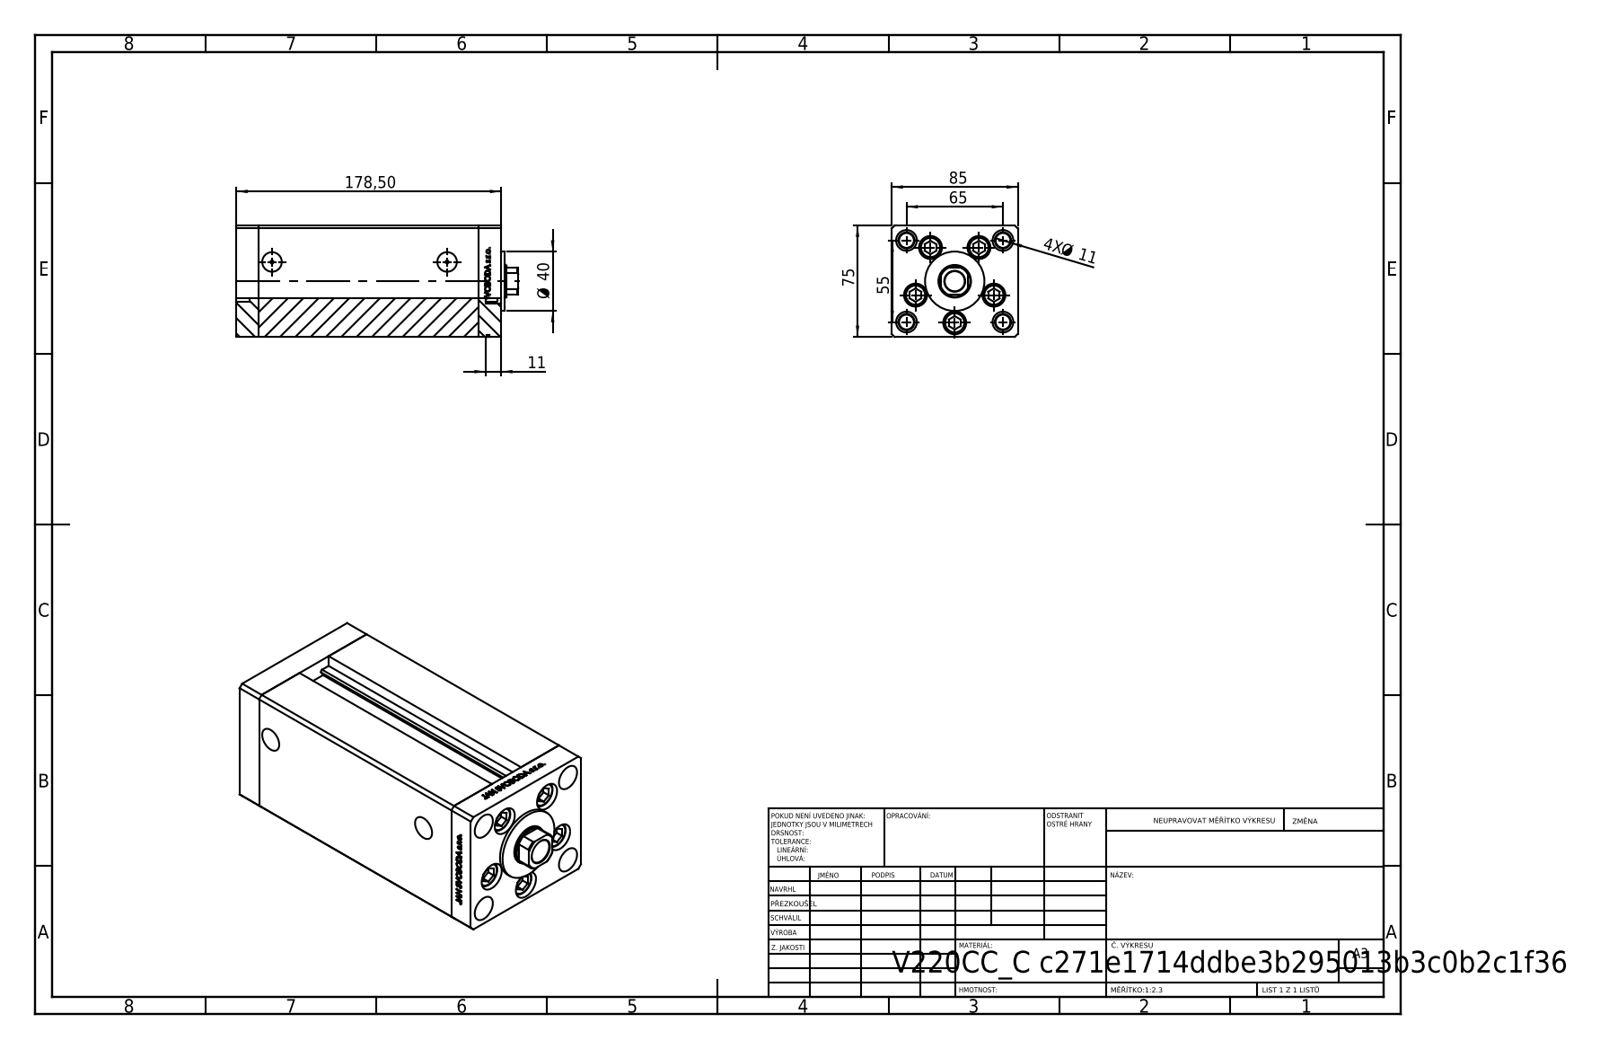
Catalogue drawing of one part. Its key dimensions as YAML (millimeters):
part_name: "V220C_VC_C; V220C_C MIDDLE; V220C FRONT; V220C BACK_C (+1 more)"
step_written_by: "SolidWorks 2019 (CONFIG_CONTROL_DESIGN)"
units: millimeters
bodies: {solids: 13, faces: 1171, planar: 542, cylindrical: 167, other: 462}
overall_size: [190, 85, 75]
volume: 945382
surface_area: 180492
round_holes:
  - {diameter: 11, count: 9}
  - {diameter: 15.5, count: 5}
  - {diameter: 10, count: 4}
  - {diameter: 14, count: 4}
  - {diameter: 2, count: 2}
  - {diameter: 13.16, count: 2}
  - {diameter: 13.5, count: 1}
  - {diameter: 14.5, count: 1}
  - {diameter: 22, count: 1}
round_bosses_or_shafts:
  - {diameter: 8, count: 5}
  - {diameter: 14.5, count: 4}
  - {diameter: 40, count: 1}
partial_cylinders:
  - {radius: 0.93, count: 2}
  - {radius: 10.5, count: 1}
face_to_face_distances: [85, 75, 15, 148.5, 163.5, 10.5, 178.5, 34.25, 144.25, 129.25]
hole_center_spacings: [28, 42.57, 16.86, 19.17, 32.33, 32.5, 33.63, 37.33]
